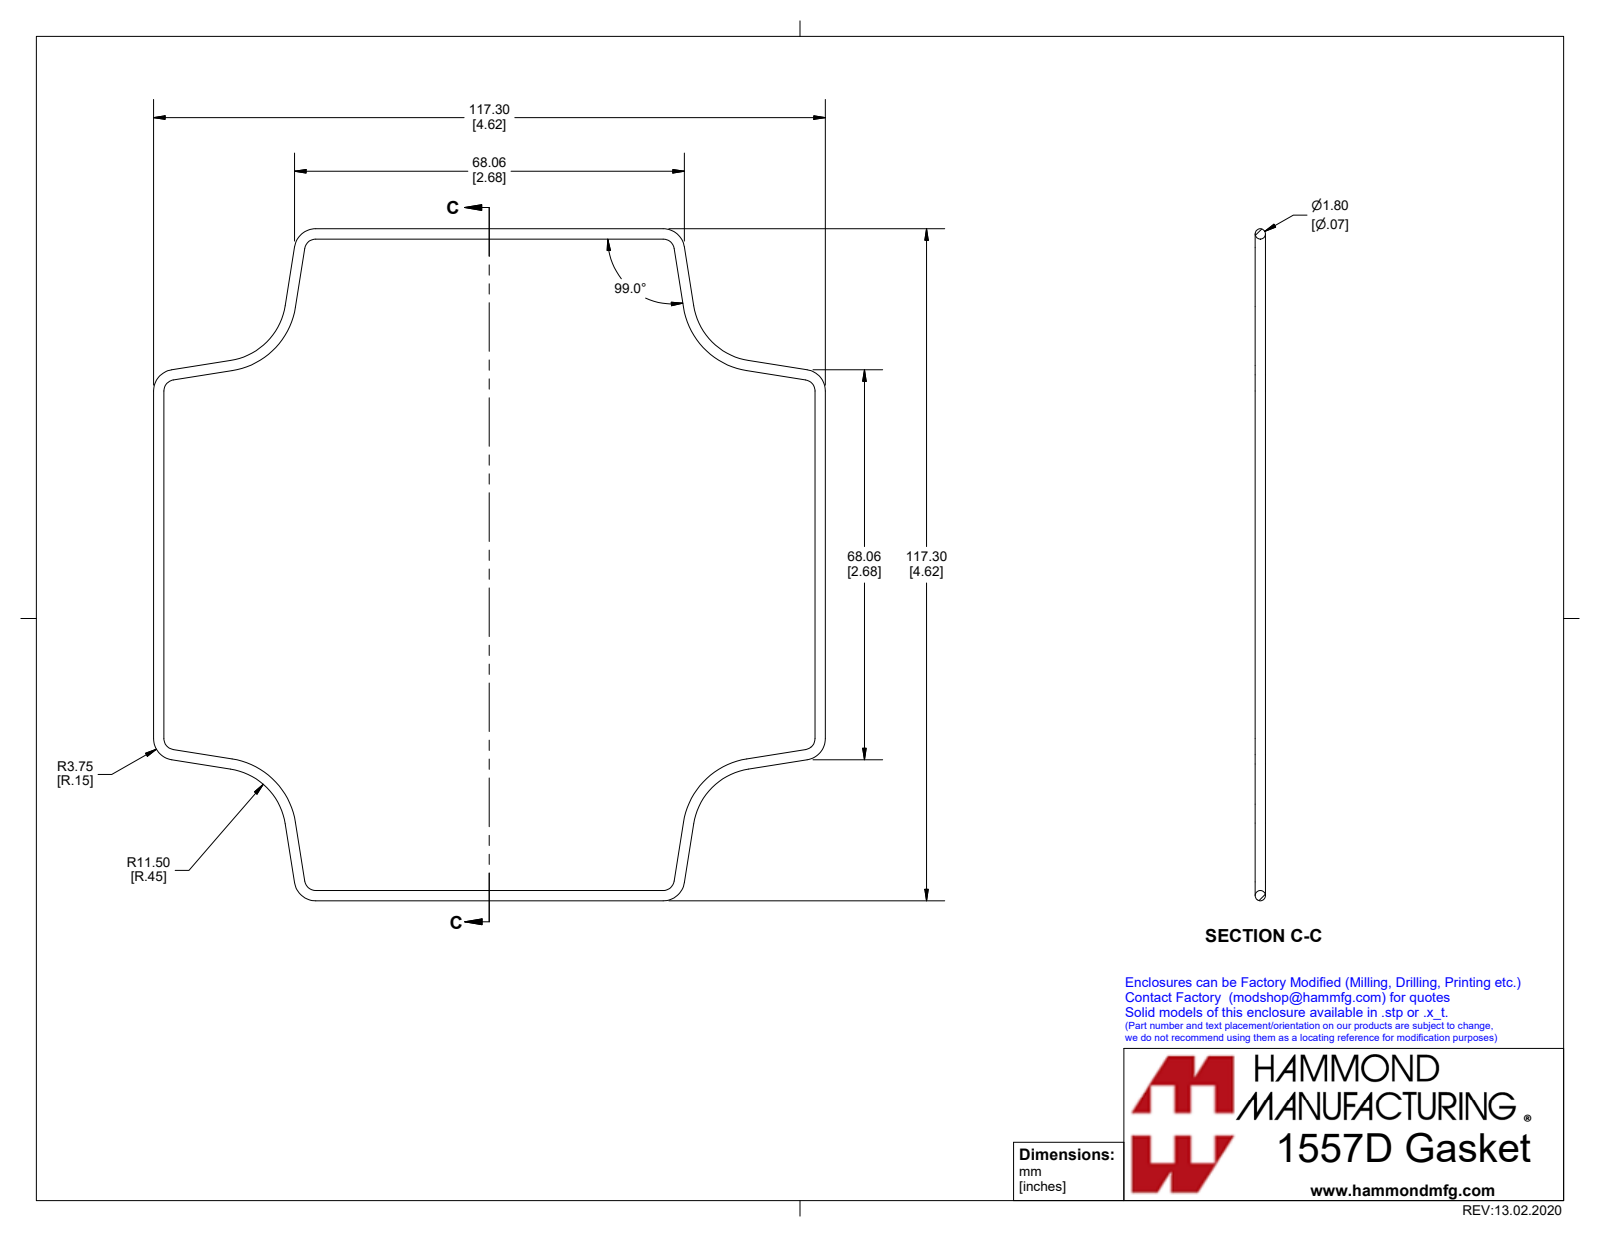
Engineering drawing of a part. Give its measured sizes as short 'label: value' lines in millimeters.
name: 1557FGASKET
written by: SolidWorks 2019 (AUTOMOTIVE_DESIGN)
unit: mm
bodies: 1 solid, 146 faces (26 planar, 56 cylindrical, 64 other)
size: 157.29 × 157.29 × 1.8
volume: 1 561 mm³; area: 3 381 mm²
rounds: 48× R0.8, 4× R11.5, 4× R13.3
face distances: 1.8, 155.5, 155.49, 157.29, 153.7, 157.3, 153.69, 128.52, 128.53, 130.32
